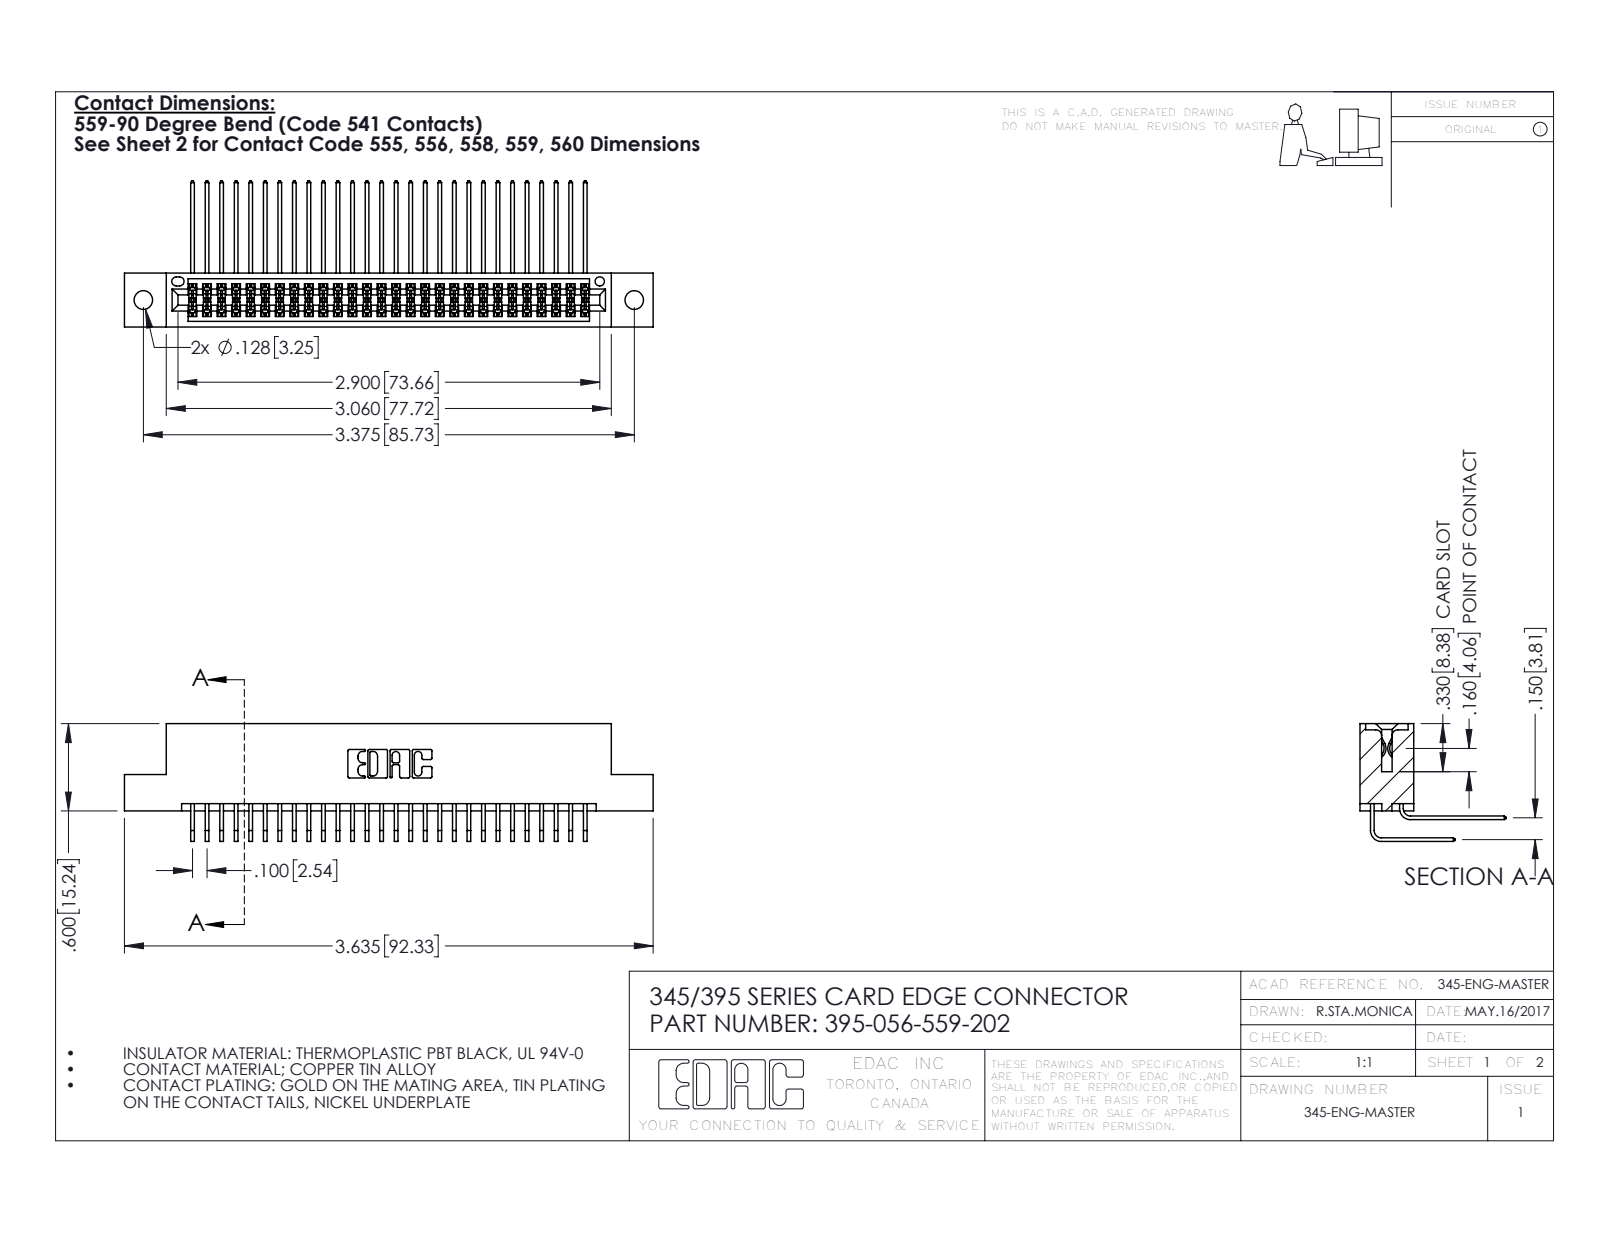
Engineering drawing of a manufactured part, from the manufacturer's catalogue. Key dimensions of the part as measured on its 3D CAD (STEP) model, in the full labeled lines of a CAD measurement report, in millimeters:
Part name (STEP PRODUCT): 345 Part_Flush Mounting Lugs - 0.128 Dia; 395-056-559-202; 345-292-001_559 Tail - 2; 345-292-001_558 559 Tail - 1
STEP written by: SolidWorks 2016 (CONFIG_CONTROL_DESIGN)
Units: millimetres
Bodies: 57 solids, 3038 faces (2040 planar, 998 cylindrical, 0 other)
Overall size (bounding box): 92.3 × 25.5 × 20.5
Volume: 9 130 mm³ · Surface area: 14 460 mm²
Round holes (diameter × count): ⌀3.3 ×2, ⌀1.6 ×1
Partial cylindrical surfaces — rounded edges, fillets, slot ends (radius × count): R0.2 ×112, R0.3 ×22, R0.2 ×6, R0.8 ×6, R0.7 ×3, R0.4 ×2, R0.5 ×2, R0.6 ×2
Main face-to-face distances: 1.8, 7.6, 5.1, 9.4, 2.5, 6.9, 0.6, 5.7, 3.8, 4.4
Hole centre spacings: 6.9, 79.8, 85.7
